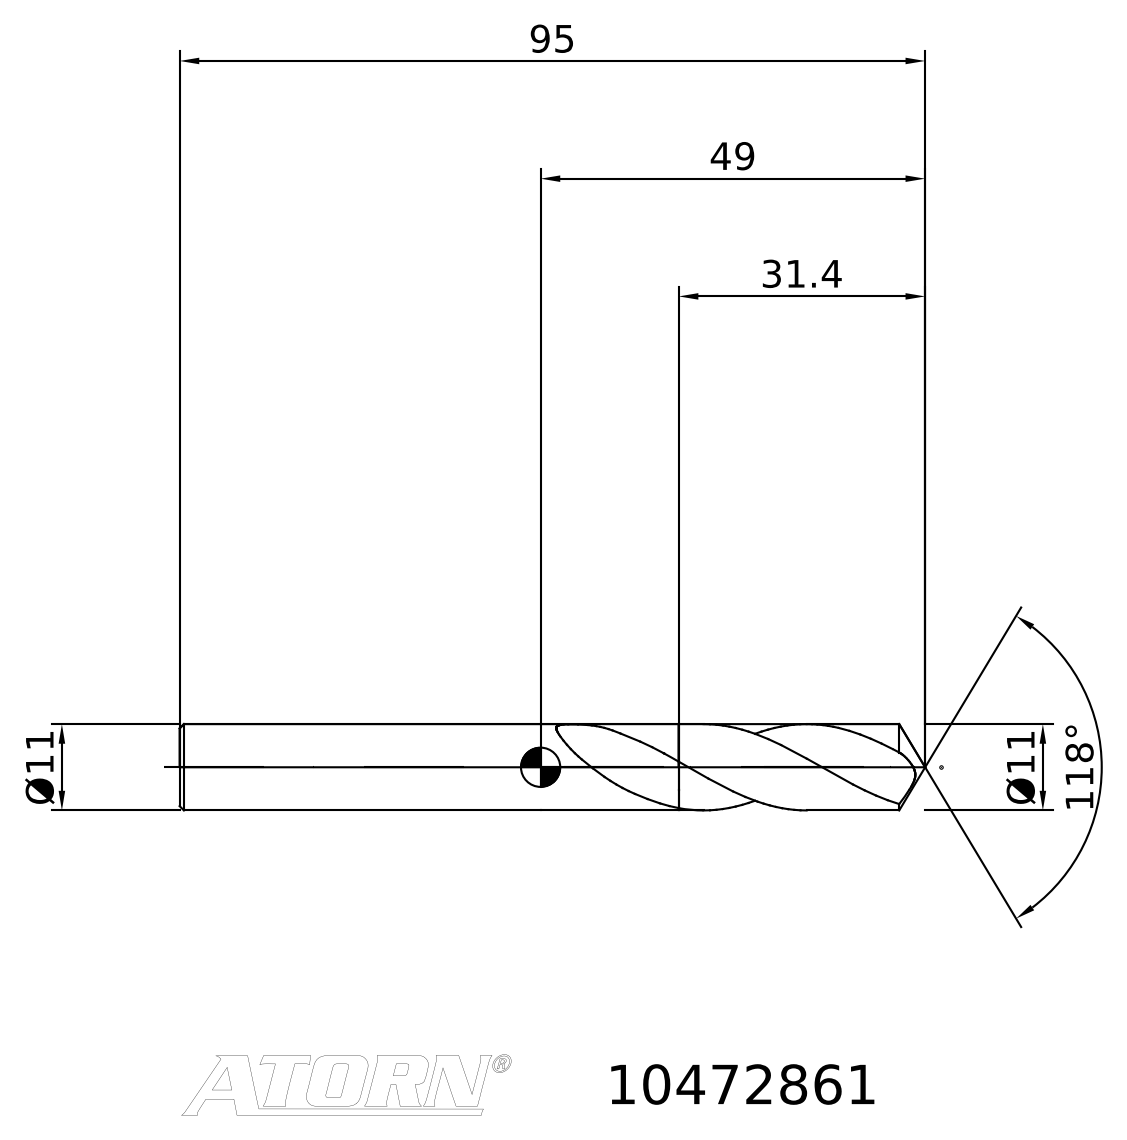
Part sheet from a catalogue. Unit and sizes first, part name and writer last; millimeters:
Units: millimetres
Overall size (bounding box): 95 × 15.04 × 11
Main face-to-face distances: 63.6
Volume: 7 472 mm³ · Surface area: 3 602 mm²
Bodies: 2 solids, 22 faces (3 planar, 0 cylindrical, 19 other)
STEP written by: TDM (AUTOMOTIVE_DESIGN)
